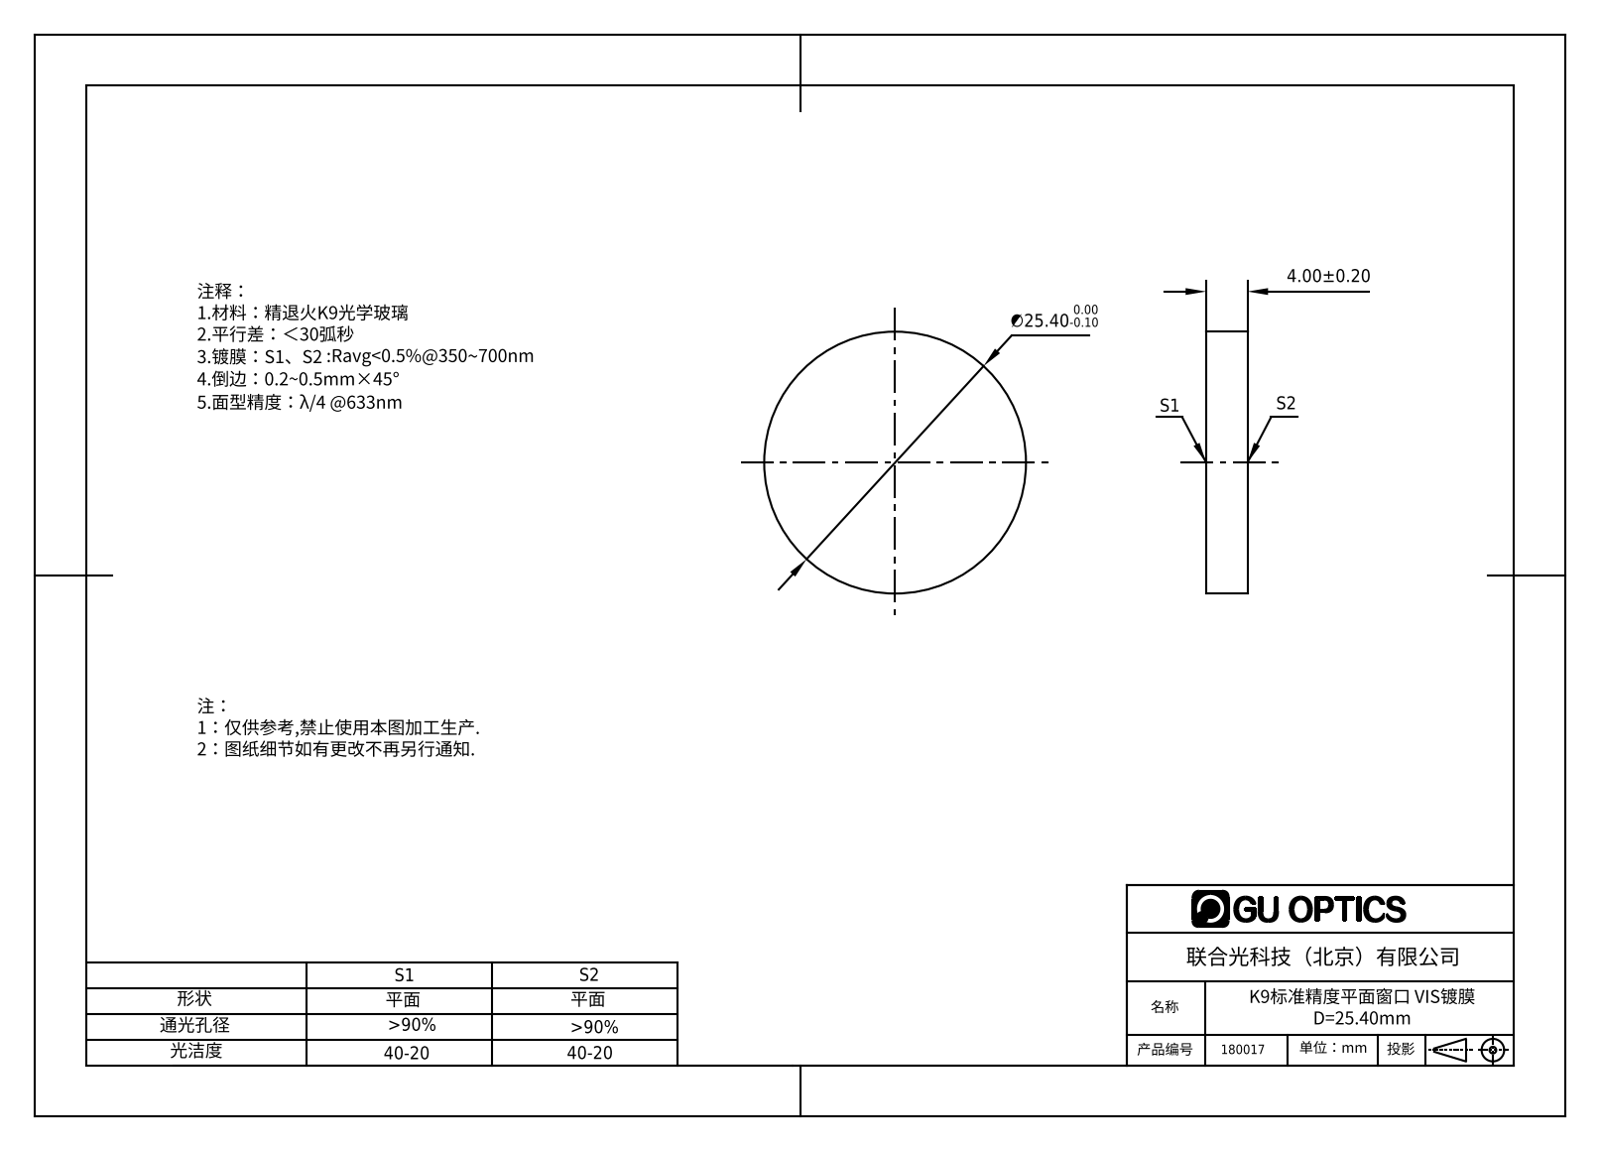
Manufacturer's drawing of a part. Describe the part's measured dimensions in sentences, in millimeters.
The part is named "180006". Its 3-D file was written by "SolidWorks 2016 (AUTOMOTIVE_DESIGN)". It is 1 solid with 4 faces: 2 planar, 2 cylindrical and 0 other. Overall it measures 25.4 by 25.4 by 4 millimeters. Its volume is 2 027 cubic millimeters and its surface area 1 333 square millimeters. Round bosses or shafts: 1 of diameter 25.4. The main face-to-face distances are 4.
